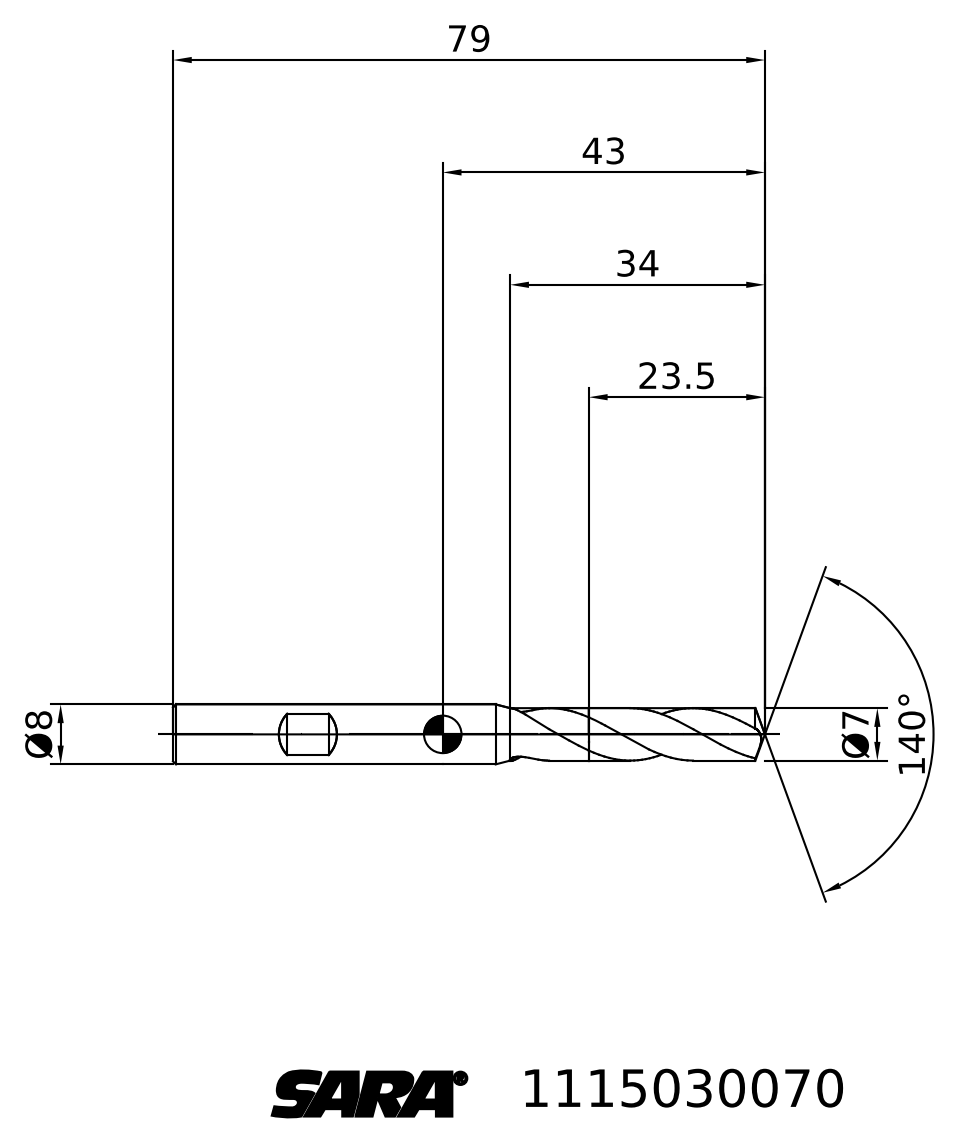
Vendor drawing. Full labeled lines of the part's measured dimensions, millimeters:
STEP written by: TDM (AUTOMOTIVE_DESIGN)
Units: millimetres
Bodies: 2 solids, 27 faces (3 planar, 0 cylindrical, 24 other)
Overall size (bounding box): 79 × 8 × 8
Volume: 3 115 mm³ · Surface area: 2 039 mm²
Main face-to-face distances: 55.5
